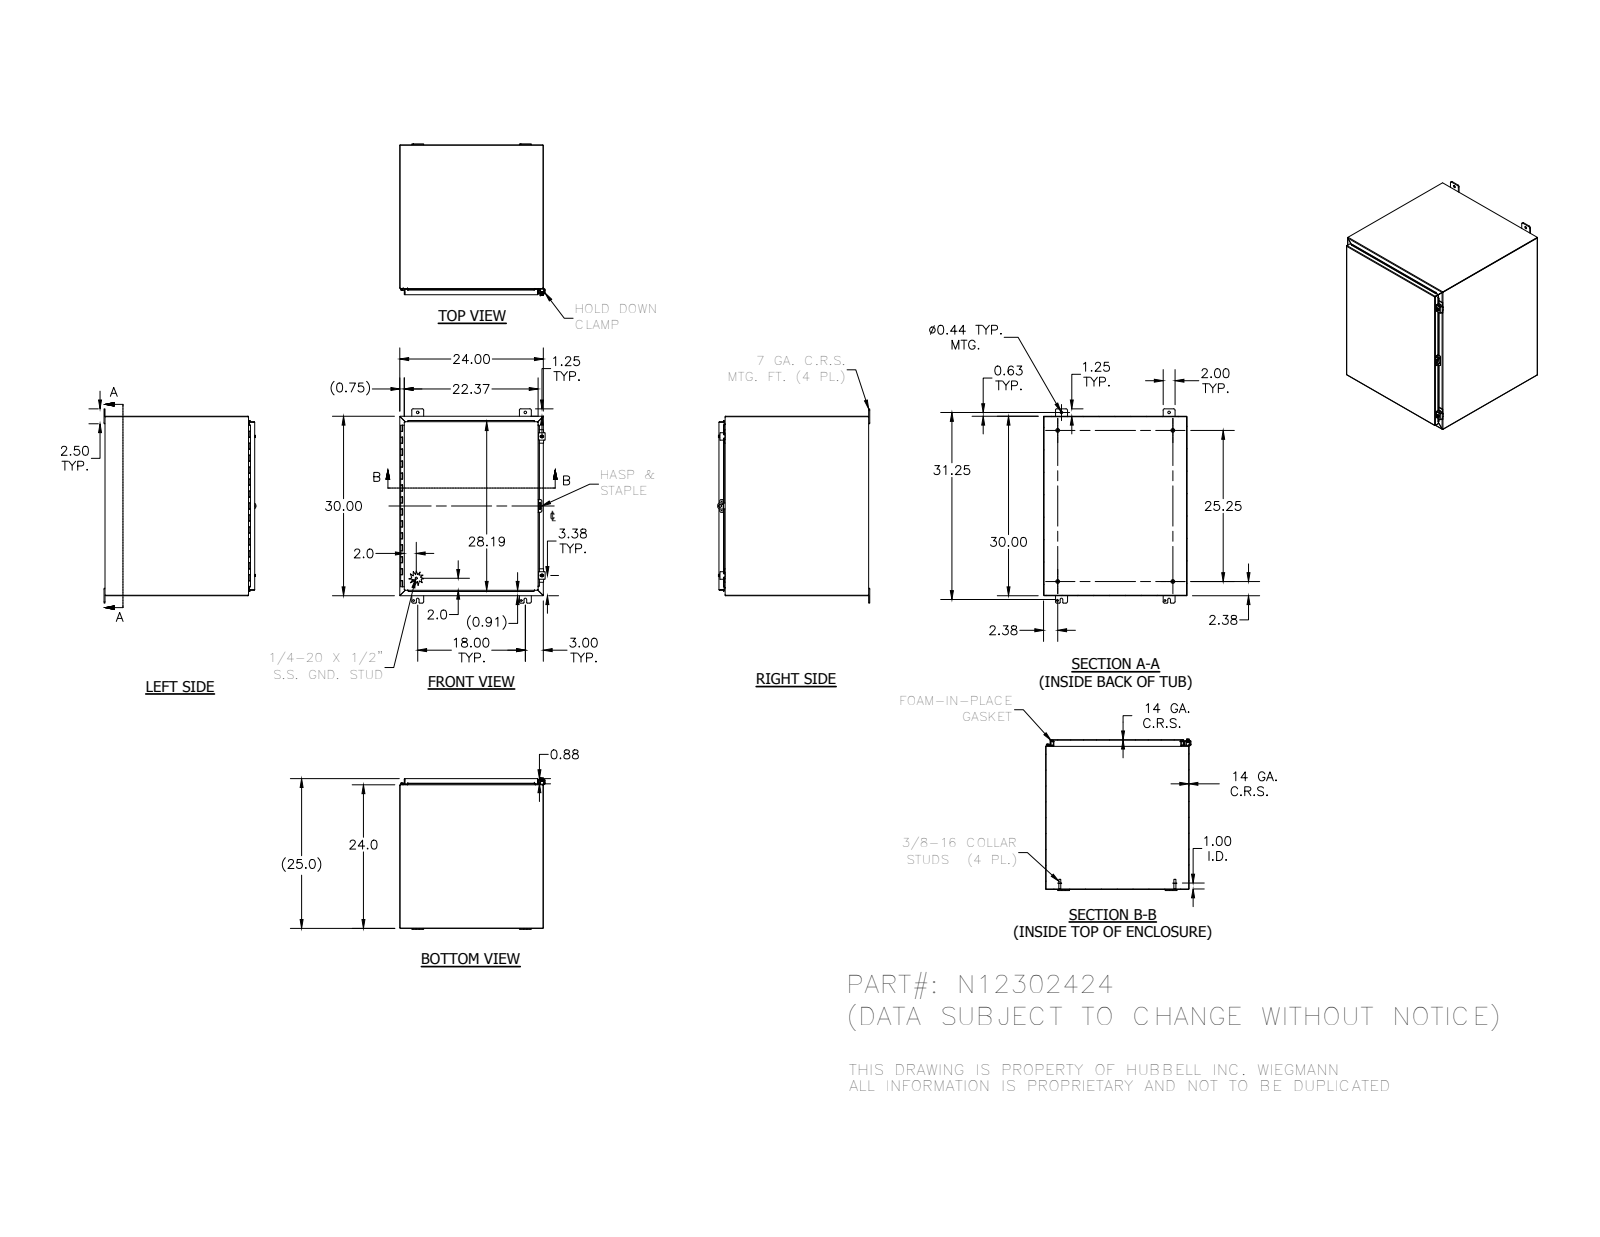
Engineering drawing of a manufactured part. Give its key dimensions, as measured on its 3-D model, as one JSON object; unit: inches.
{"part_name": "N12302424; 34840; 38413; N122424TB (+8 more)", "step_written_by": "Autodesk Inventor 2012 (AUTOMOTIVE_DESIGN)", "units": "inches", "bodies": {"solids": 29, "faces": 918, "planar": 540, "cylindrical": 277, "other": 101}, "overall_size": [32.5, 25.41, 24.311], "volume_in3": 333.3, "surface_area_in2": 8856, "round_holes": [[0.313, 4], [0.438, 4], [0.11, 3], [0.211, 2], [0.281, 2], [0.3, 2], [0.125, 1], [0.156, 1], [0.5, 1]], "round_bosses_or_shafts": [[0.625, 4], [0.33, 4], [0.25, 4], [0.52, 2], [0.5, 2], [0.35, 2], [0.115, 2], [0.337, 1]], "partial_cylinders_radius": [[0.03, 27], [0.125, 25], [0.25, 25], [0.031, 21], [0.105, 21], [0.063, 13], [0.1, 4], [0.141, 4]], "face_to_face_distances": [0.074, 23.926, 24.959, 29.926, 24, 23.852, 24.885, 25.033, 29.852, 30], "hole_center_spacings": [1.593, 18, 30, 34.986, 0.791, 17.372, 18.742, 28.571]}
